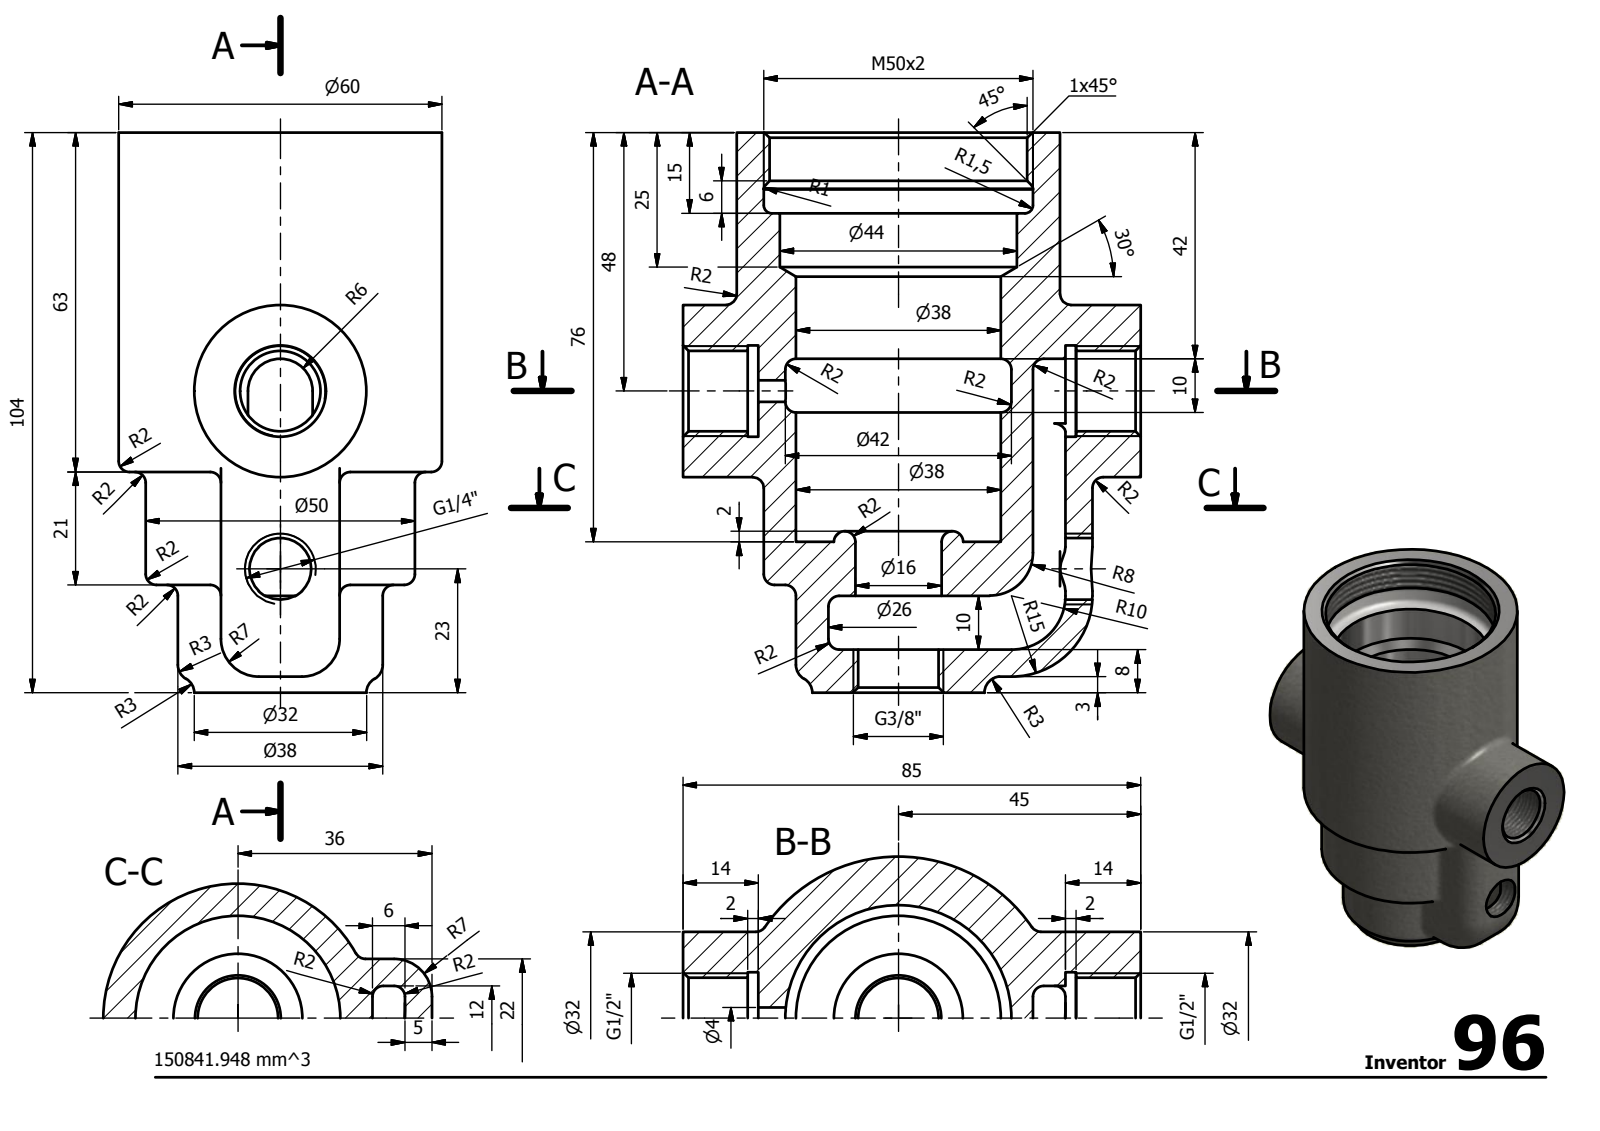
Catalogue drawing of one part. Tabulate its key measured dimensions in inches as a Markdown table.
| quantity | value |
| --- | --- |
| STEP written by | Autodesk Inventor 2014 (AUTOMOTIVE_DESIGN) |
| units | inches |
| bodies | 1 solid, 140 faces (27 planar, 52 cylindrical, 61 other) |
| overall size | 4.094 × 3.346 × 2.362 |
| volume | 9.205 in³ |
| surface area | 64.09 in² |
| round holes (diameter × count) | 0.589 × 2, 0.157 × 1, 0.451 × 1, 0.63 × 1, 0.669 × 1, 1.024 × 1, 1.496 × 1, 1.654 × 1, 1.732 × 1, 1.883 × 1, 1.969 × 1 |
| round bosses / shafts (diameter × count) | 2.362 × 1, 1.26 × 1 |
| partial cylindrical surfaces (radius × count) | 0.079 × 22, 0.276 × 4, 0.236 × 1, 0.315 × 1, 0.394 × 1, 0.591 × 1 |
| main face-to-face distances | 0.787, 2.992, 2.795, 1.102, 4.094, 3.346, 0.315, 0.472, 0.197, 0.394 |
| hole center spacings | 1.299 |
